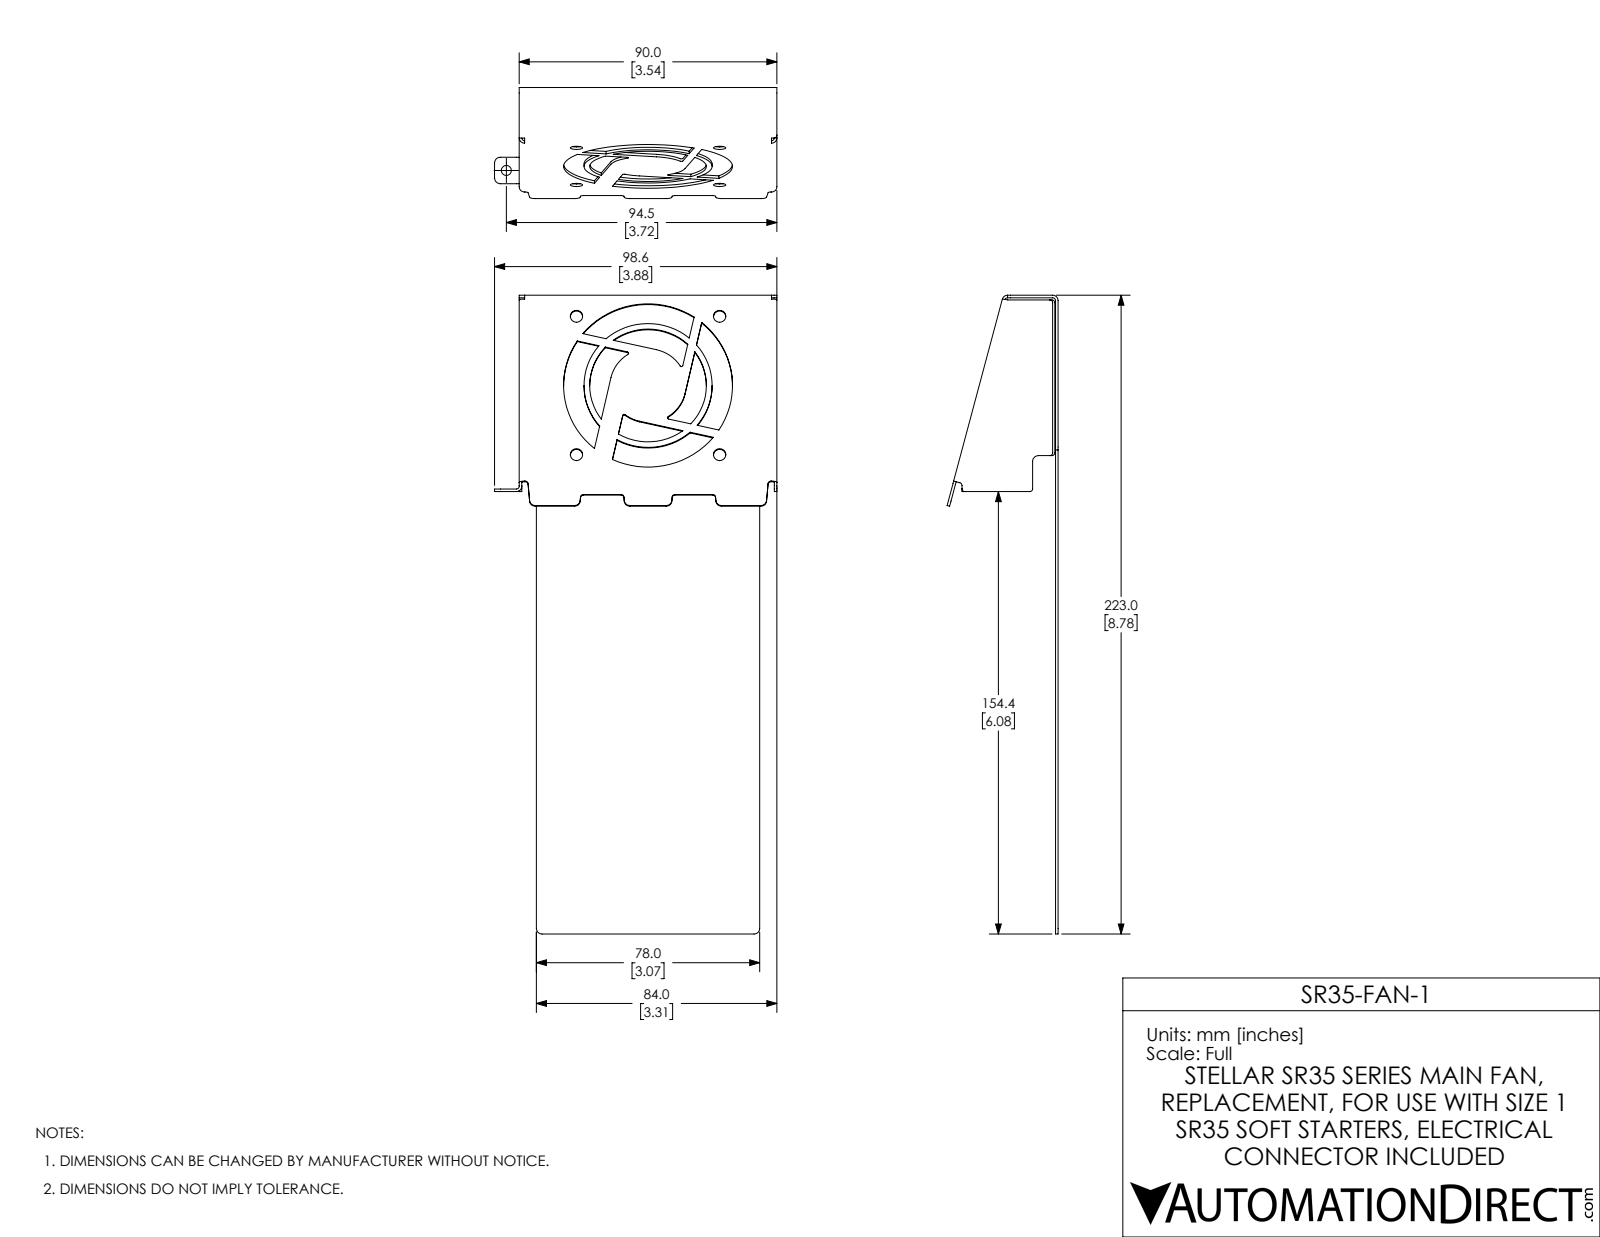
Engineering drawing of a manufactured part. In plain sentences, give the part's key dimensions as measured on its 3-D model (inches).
The part is named "STP-AGY-004-V01 (AGY1 FAN) Coord fXT". Its 3-D file was written by "SolidWorks 2017 (AUTOMOTIVE_DESIGN)". It is 1 solid with 145 faces: 68 planar, 75 cylindrical and 2 other. Overall it measures 8.78 by 3.882 by 1.526 inches. Its volume is 1.525 cubic inches and its surface area 88.3 square inches. Round holes: 4 of diameter 0.169, 1 of diameter 0.138, 1 of diameter 1.604, 1 of diameter 2.323. Round bosses or shafts: 1 of diameter 1.762. Partial cylindrical surfaces (rounded edges, fillets, slot ends): 22 of radius 0.039, 11 of radius 0.079, 5 of radius 0.075, 4 of radius 0.02, 1 of radius 0.522. The main face-to-face distances are 0.035, 3.508, 3.543, 3.472, 0.236, 3.307, 0.201, 3.272, 3.071, 2.663. The hole center spacings are 1.392, 1.392, 1.969, 1.969, 2.784.
